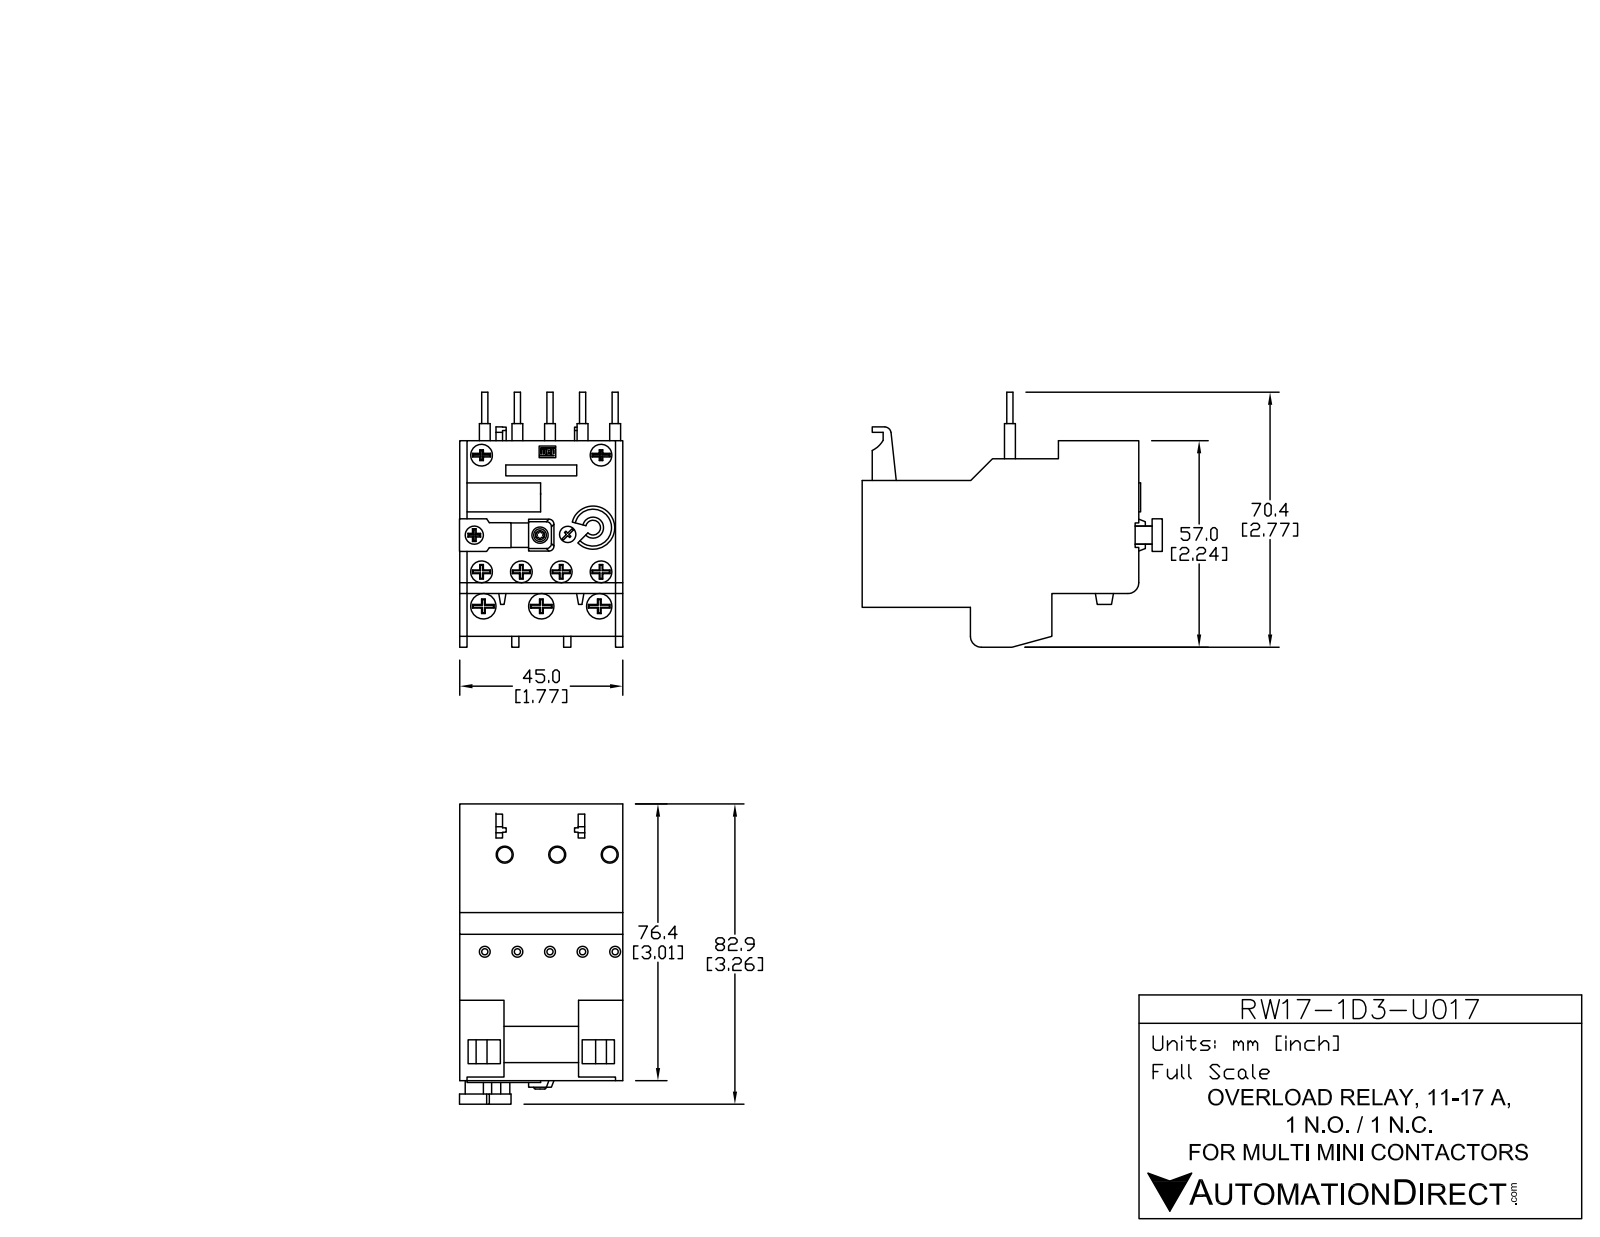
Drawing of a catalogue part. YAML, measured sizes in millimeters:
part_name: "RW17D-1D3-U017"
step_written_by: "SolidWorks 2013 (AUTOMOTIVE_DESIGN)"
units: millimeters
bodies: {solids: 18, faces: 756, planar: 515, cylindrical: 214, other: 27}
overall_size: [82.65, 70.5, 45.55]
volume: 127454
surface_area: 34704
round_holes:
  - {diameter: 6, count: 6}
  - {diameter: 4, count: 3}
  - {diameter: 7, count: 3}
  - {diameter: 7.5, count: 3}
  - {diameter: 4.5, count: 1}
  - {diameter: 4.75, count: 1}
  - {diameter: 5.33, count: 1}
  - {diameter: 5.5, count: 1}
  - {diameter: 10.42, count: 1}
round_bosses_or_shafts:
  - {diameter: 5.5, count: 7}
  - {diameter: 3, count: 7}
  - {diameter: 1.75, count: 5}
  - {diameter: 5.6, count: 2}
  - {diameter: 3.25, count: 2}
  - {diameter: 6.42, count: 1}
  - {diameter: 6.15, count: 1}
  - {diameter: 4.75, count: 1}
partial_cylinders:
  - {radius: 0.5, count: 20}
  - {radius: 0.25, count: 12}
  - {radius: 1, count: 9}
  - {radius: 4.52, count: 6}
  - {radius: 5.86, count: 4}
  - {radius: 7.86, count: 4}
  - {radius: 1.5, count: 3}
  - {radius: 1.25, count: 2}
face_to_face_distances: [45.5, 1.5, 10.85, 11, 76.4, 35, 1.42, 74.98, 74.9, 6]
hole_center_spacings: [15, 8.55, 10.75, 30, 10.57, 11.86, 14.25, 21.35]
